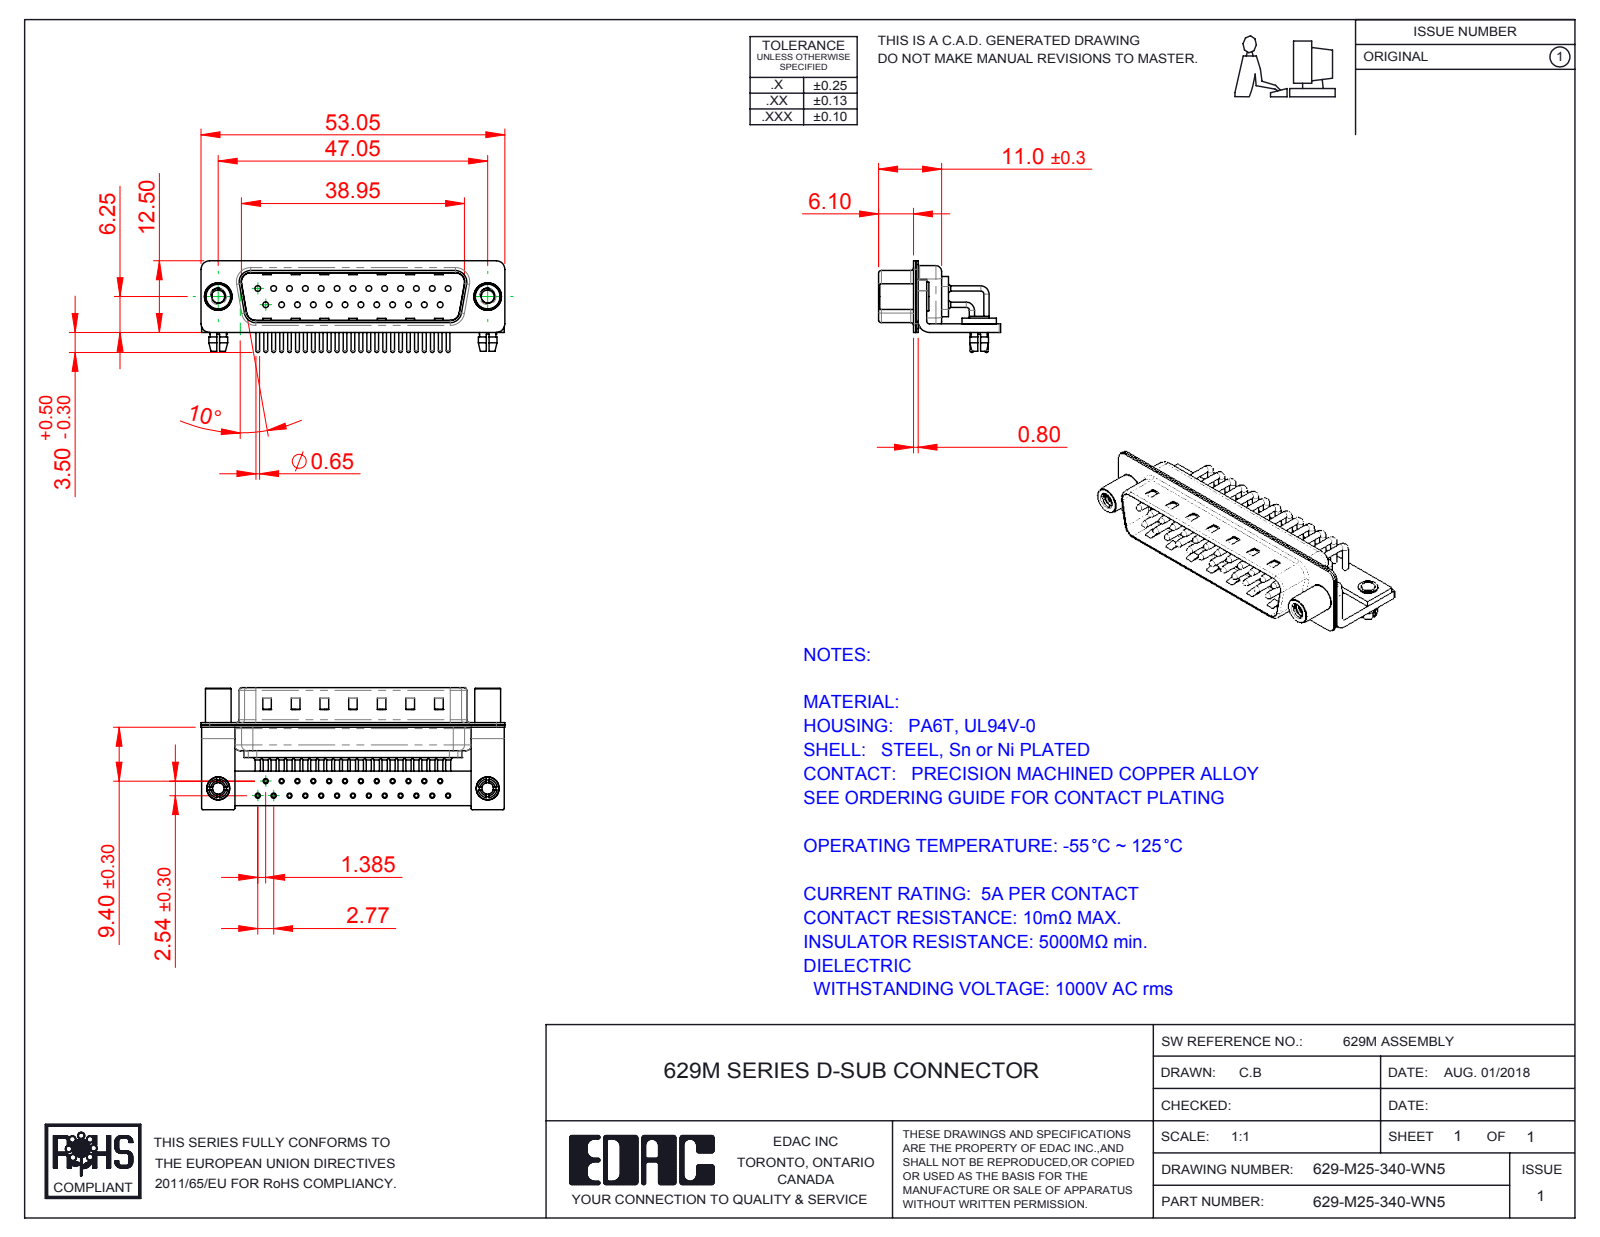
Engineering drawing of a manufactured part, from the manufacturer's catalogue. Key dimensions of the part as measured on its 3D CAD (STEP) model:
Part name (STEP PRODUCT): 629M Contact Row 2; 629M Contact Row 1; 629M Board Lock; 629M Shell Rear_25 Contacts (+6 more)
STEP written by: SolidWorks 2016 (CONFIG_CONTROL_DESIGN)
Units: millimetres
Bodies: 35 solids, 3368 faces (1847 planar, 1183 cylindrical, 338 other)
Overall size (bounding box): 53.05 × 21.3 × 16
Volume: 3 638 mm³ · Surface area: 9 694 mm²
Round holes (diameter × count): ⌀2 ×27, ⌀0.9 ×25, ⌀1 ×25, ⌀1.7 ×25, ⌀2.26 ×2, ⌀2.5 ×2, ⌀3.2 ×2, ⌀4 ×2, ⌀4.8 ×2
Round bosses / shafts (diameter × count): ⌀1.5 ×25, ⌀0.9 ×25, ⌀0.65 ×25, ⌀5 ×2, ⌀4.9 ×2, ⌀4.5 ×2, ⌀4 ×2, ⌀3.4 ×2
Partial cylindrical surfaces — rounded edges, fillets, slot ends (radius × count): R1.01 ×25, R0.25 ×16, R1.5 ×16, R2 ×13, R0.5 ×9, R1.6 ×8, R0.6 ×4, R0.65 ×4
Main face-to-face distances: 0.4, 0.85, 1.25, 1.5, 9.55, 10.4, 0.8, 8.3, 1, 1.9
Hole centre spacings: 2.77, 5.54, 8.31, 11.08, 13.85, 3.16, 4.87, 16.62
